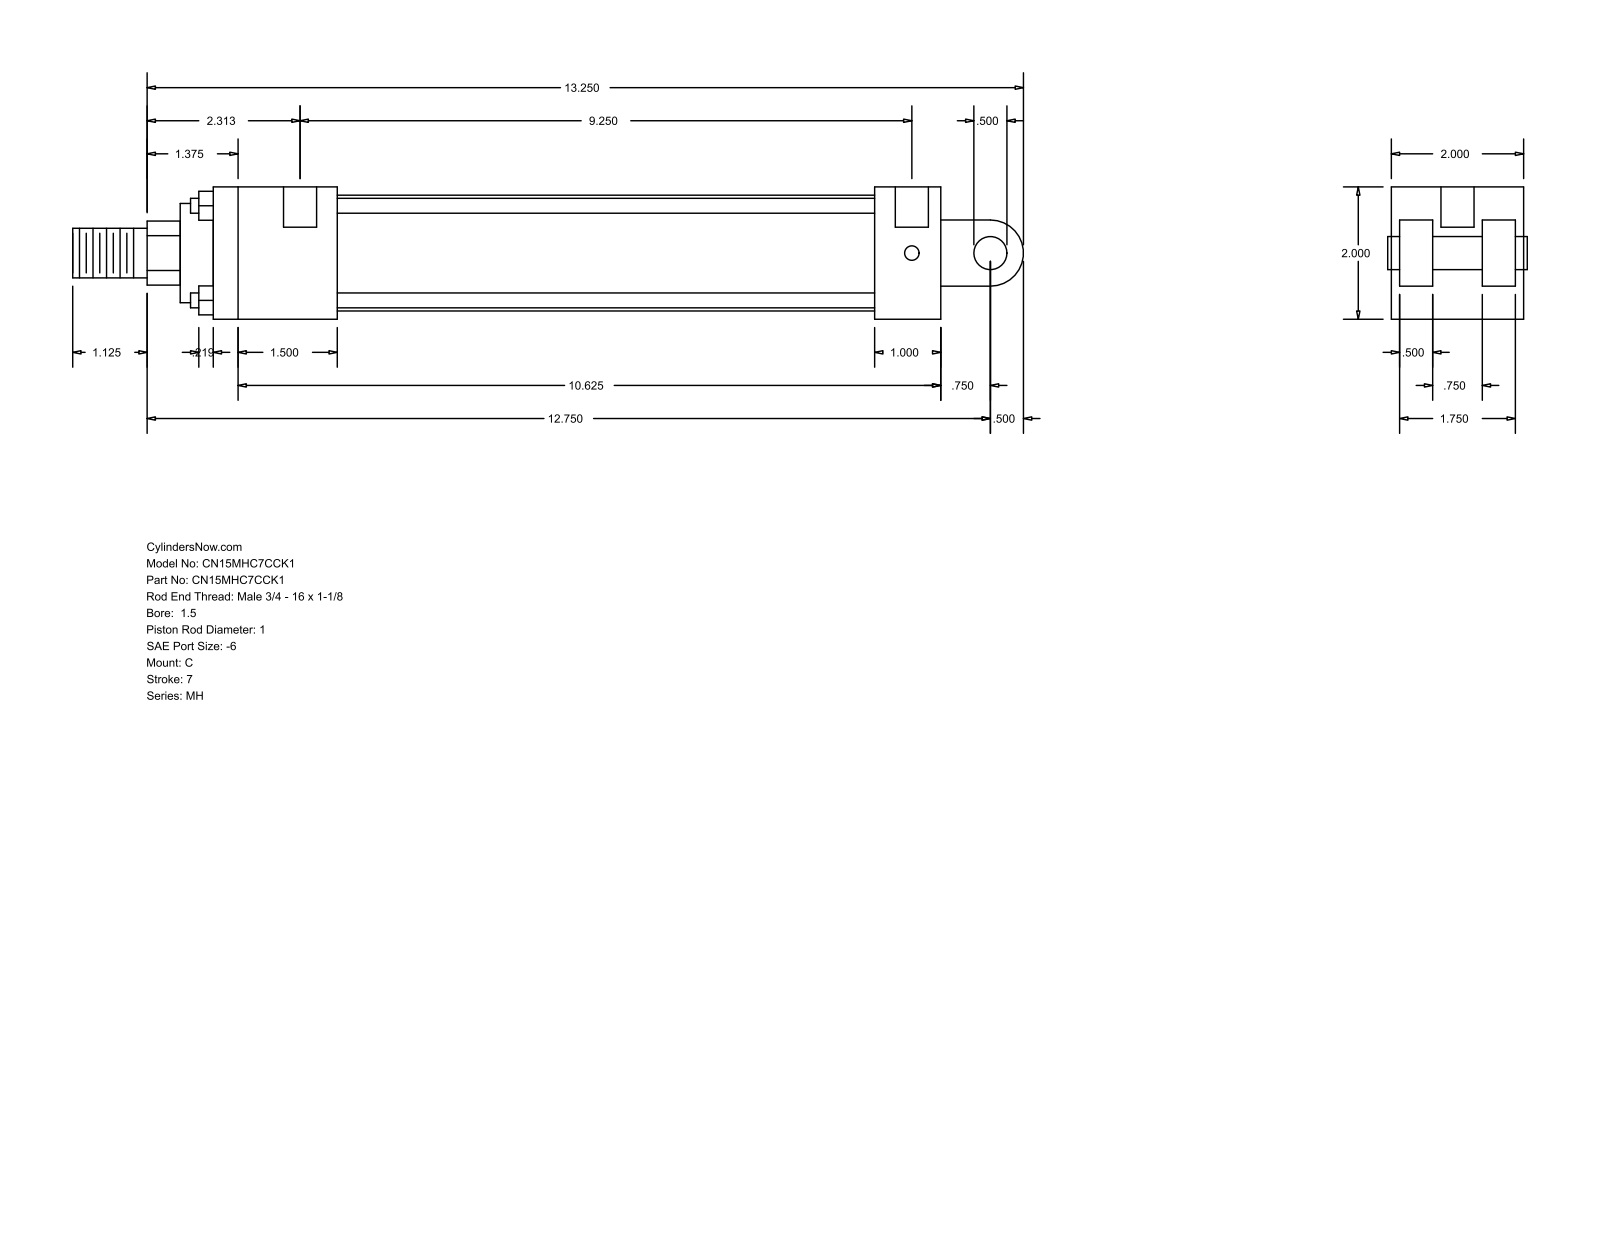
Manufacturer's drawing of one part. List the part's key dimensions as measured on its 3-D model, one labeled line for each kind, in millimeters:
Part name (STEP PRODUCT): MH_C__0150_1
STEP written by: GSSL Pune (CONFIG_CONTROL_DESIGN)
Units: millimetres
Bodies: 0 solids, 99 faces (70 planar, 29 cylindrical, 0 other)
Overall size (bounding box): 365.12 × 50.8 × 50.8
Round holes (diameter × count): ⌀5.56 ×4, ⌀12.7 ×2
Round bosses / shafts (diameter × count): ⌀5.71 ×4, ⌀44.45 ×1, ⌀38.1 ×1, ⌀25.4 ×1, ⌀19.05 ×1, ⌀12.7 ×1
Partial cylindrical surfaces — rounded edges, fillets, slot ends (radius × count): R12.29 ×1, R12.7 ×1
Main face-to-face distances: 50.8, 12.7, 47.63, 25.4, 3.17, 15.87, 34.93, 31.76, 279.4, 38.1
Hole centre spacings: 238.13, 3.18, 234.95
